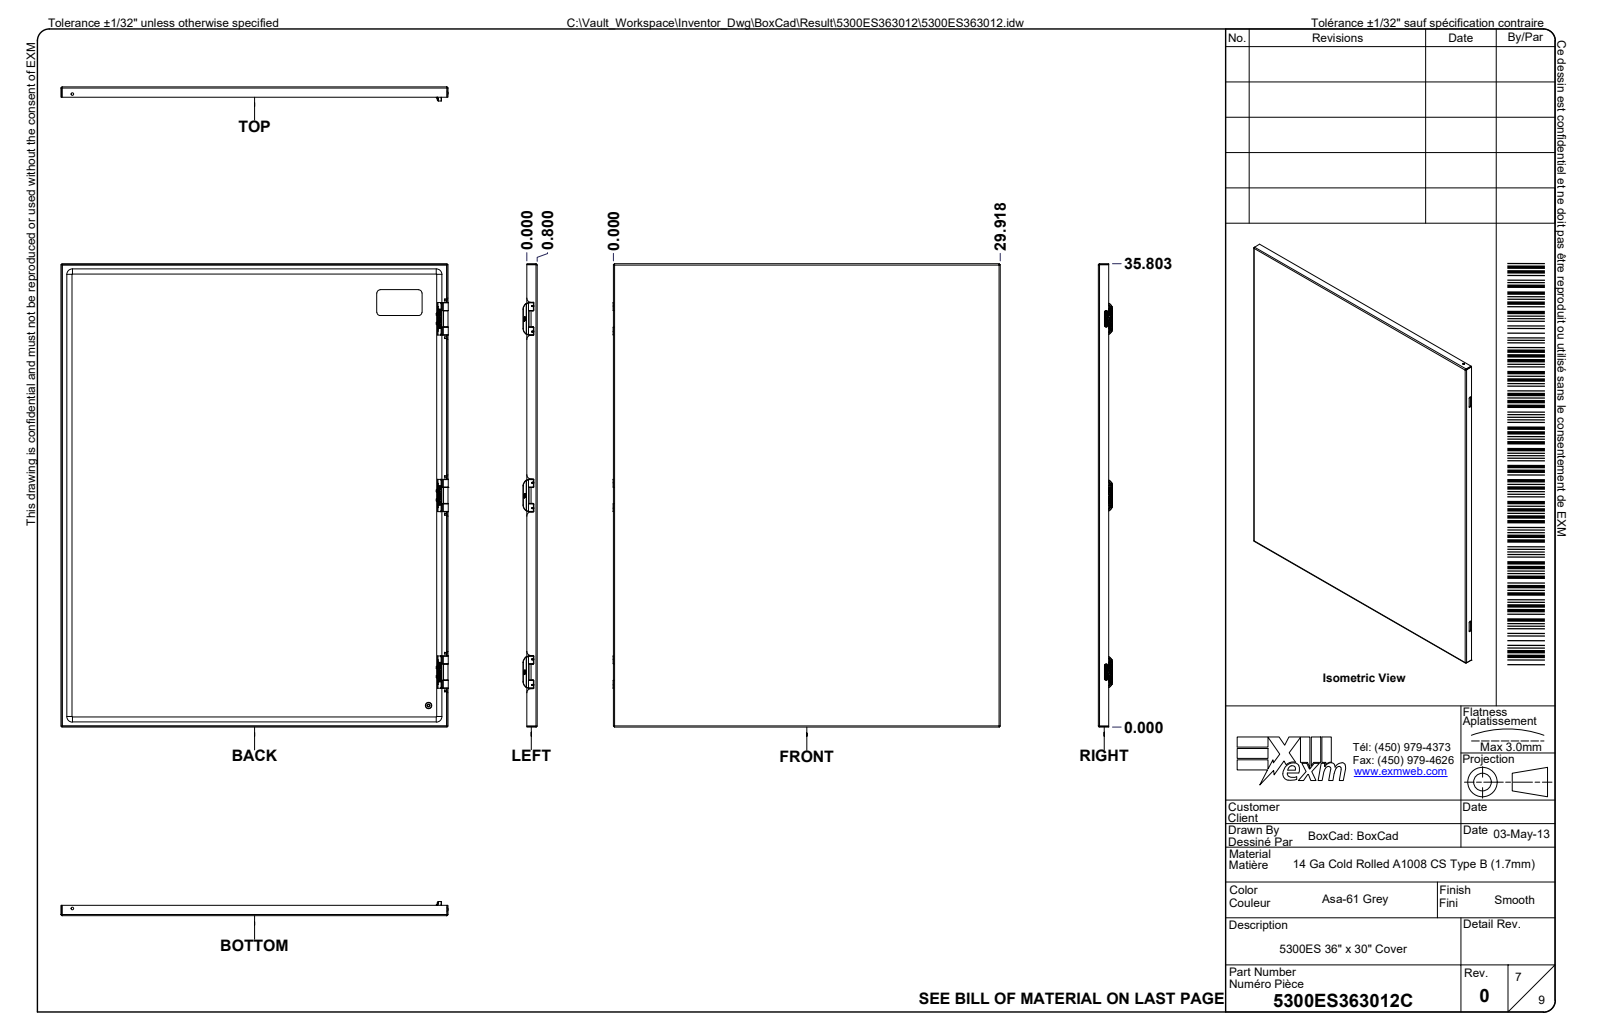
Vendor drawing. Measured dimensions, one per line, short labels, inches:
name: 5300ES363012; 5300ES363012B; 5300ES363012B-P; STK-Q-16005 (+8 more)
written by: Autodesk Inventor 2024 (AUTOMOTIVE_DESIGN)
unit: in
bodies: 69 solids, 8327 faces (2273 planar, 2340 cylindrical, 3714 other)
size: 36 × 30.938 × 13.119
volume: 395.8 in³; area: 10 437 in²
holes: 12× ⌀0.043, 8× ⌀0.03, 8× ⌀0.315, 6× ⌀0.178, 6× ⌀0.27, 5× ⌀0.201, 4× ⌀0.29, 4× ⌀0.39, 3× ⌀0.187, 3× ⌀0.22, 3× ⌀0.33, 2× ⌀0.197
bosses: 12× ⌀0.039, 8× ⌀0.03, 7× ⌀0.232, 6× ⌀0.717, 6× ⌀0.311, 6× ⌀0.262, 3× ⌀0.472, 3× ⌀0.287
rounds: 121× R0.02, 121× R0.039, 96× R0.01, 90× R0.008, 48× R0.031, 44× R0.016, 28× R0.099, 24× R0.004
face distances: 0.068, 13.052, 12.983, 13.12, 0.942, 0.874, 12.109, 12.178, 1.047, 0.979
hole spacings: 13.652, 27.303, 16.125, 0.35, 0.735, 1.052, 1.385, 1.969
